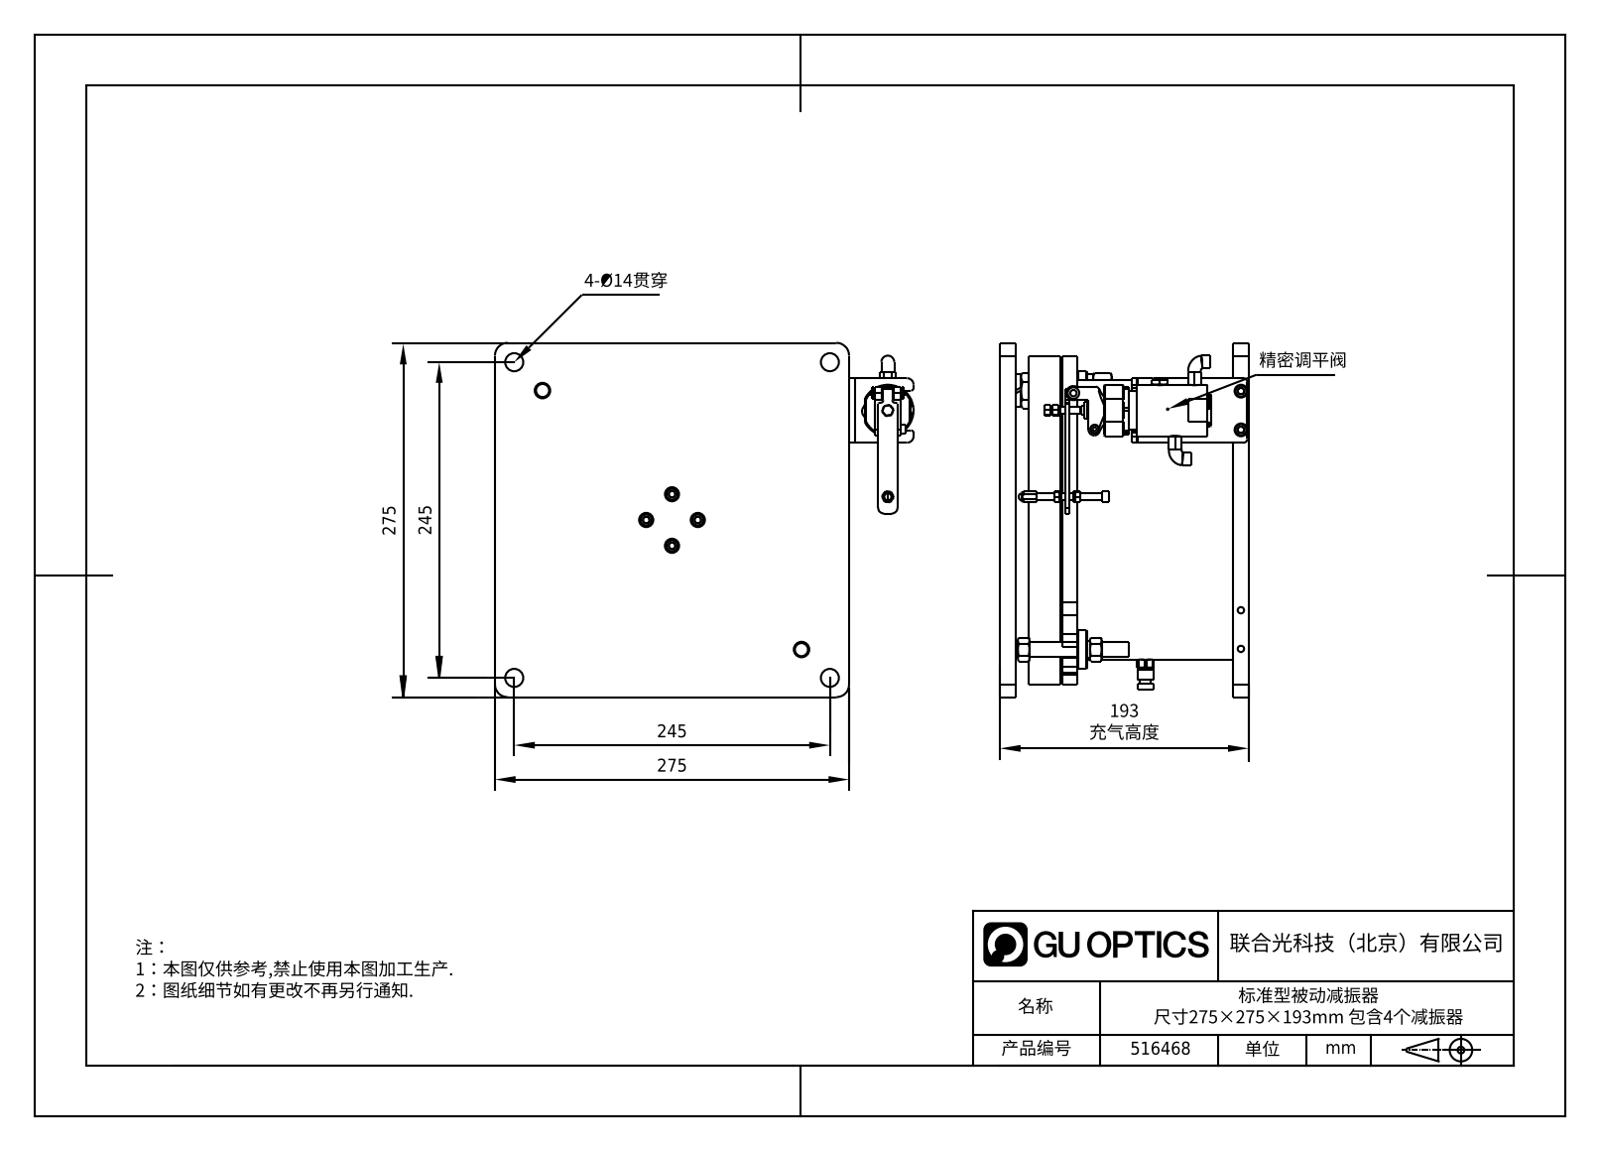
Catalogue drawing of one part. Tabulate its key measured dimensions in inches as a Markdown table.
| quantity | value |
| --- | --- |
| part name | 516468 |
| STEP written by | SolidWorks 2020 (CONFIG_CONTROL_DESIGN) |
| units | inches |
| bodies | 0 solids, 493 faces (279 planar, 146 cylindrical, 68 other) |
| overall size | 12.795 × 10.827 × 7.598 |
| round holes (diameter × count) | 0.197 × 4, 0.551 × 4, 0.382 × 3, 0.512 × 2, 0.315 × 1, 0.433 × 1, 0.453 × 1, 0.5 × 1, 10.039 × 1 |
| round bosses / shafts (diameter × count) | 0.472 × 5, 0.433 × 4, 1.181 × 3, 0.496 × 3, 0.409 × 3, 0.333 × 3, 0.319 × 3, 0.236 × 3 |
| partial cylindrical surfaces (radius × count) | 0.197 × 10, 0.394 × 8, 0.079 × 4, 0.012 × 3, 0.276 × 3, 0.118 × 2, 0.177 × 2, 0.433 × 2 |
| main face-to-face distances | 0.472, 7.126, 6.654, 7.598, 1.89, 5.236, 4.764, 2.362, 1.417, 5.709 |
| hole center spacings | 6.82, 9.646, 8.822, 13.641, 1.181, 1.225, 1.575, 2.306 |
